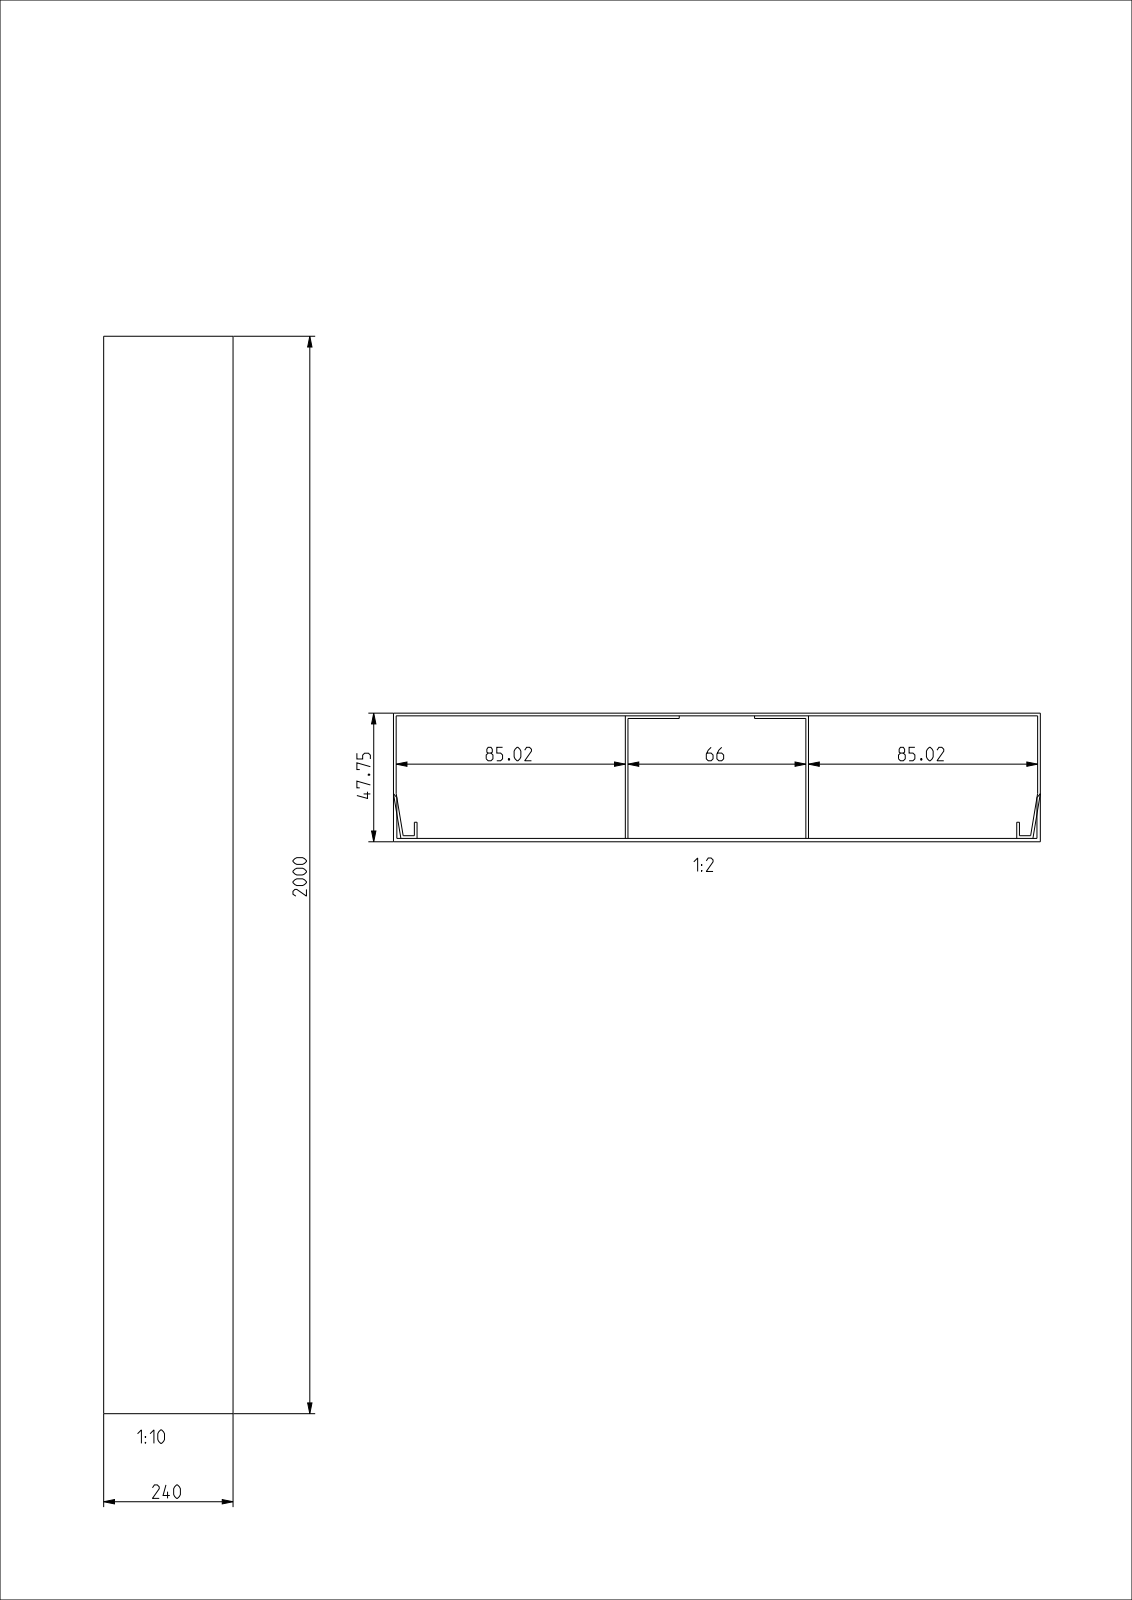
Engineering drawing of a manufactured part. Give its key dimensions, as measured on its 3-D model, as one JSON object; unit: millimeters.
{"part_name": "UK240483KUN_OBERTEIL; UK240483KUN_UNTERTEIL; UK240483KUN_ASM", "step_written_by": "CREO PARAMETRIC BY PTC INC, 2022024 (AUTOMOTIVE_DESIGN)", "units": "millimeters", "bodies": {"solids": 2, "faces": 46, "planar": 46, "cylindrical": 0, "other": 0}, "overall_size": [2000, 240, 47.75], "volume_mm3": 1634000, "surface_area_mm2": 2870000, "face_to_face_distances": [1, 1.25, 46.5, 47.75, 45.5, 46.75, 0.98, 86.02, 153.98, 87]}
